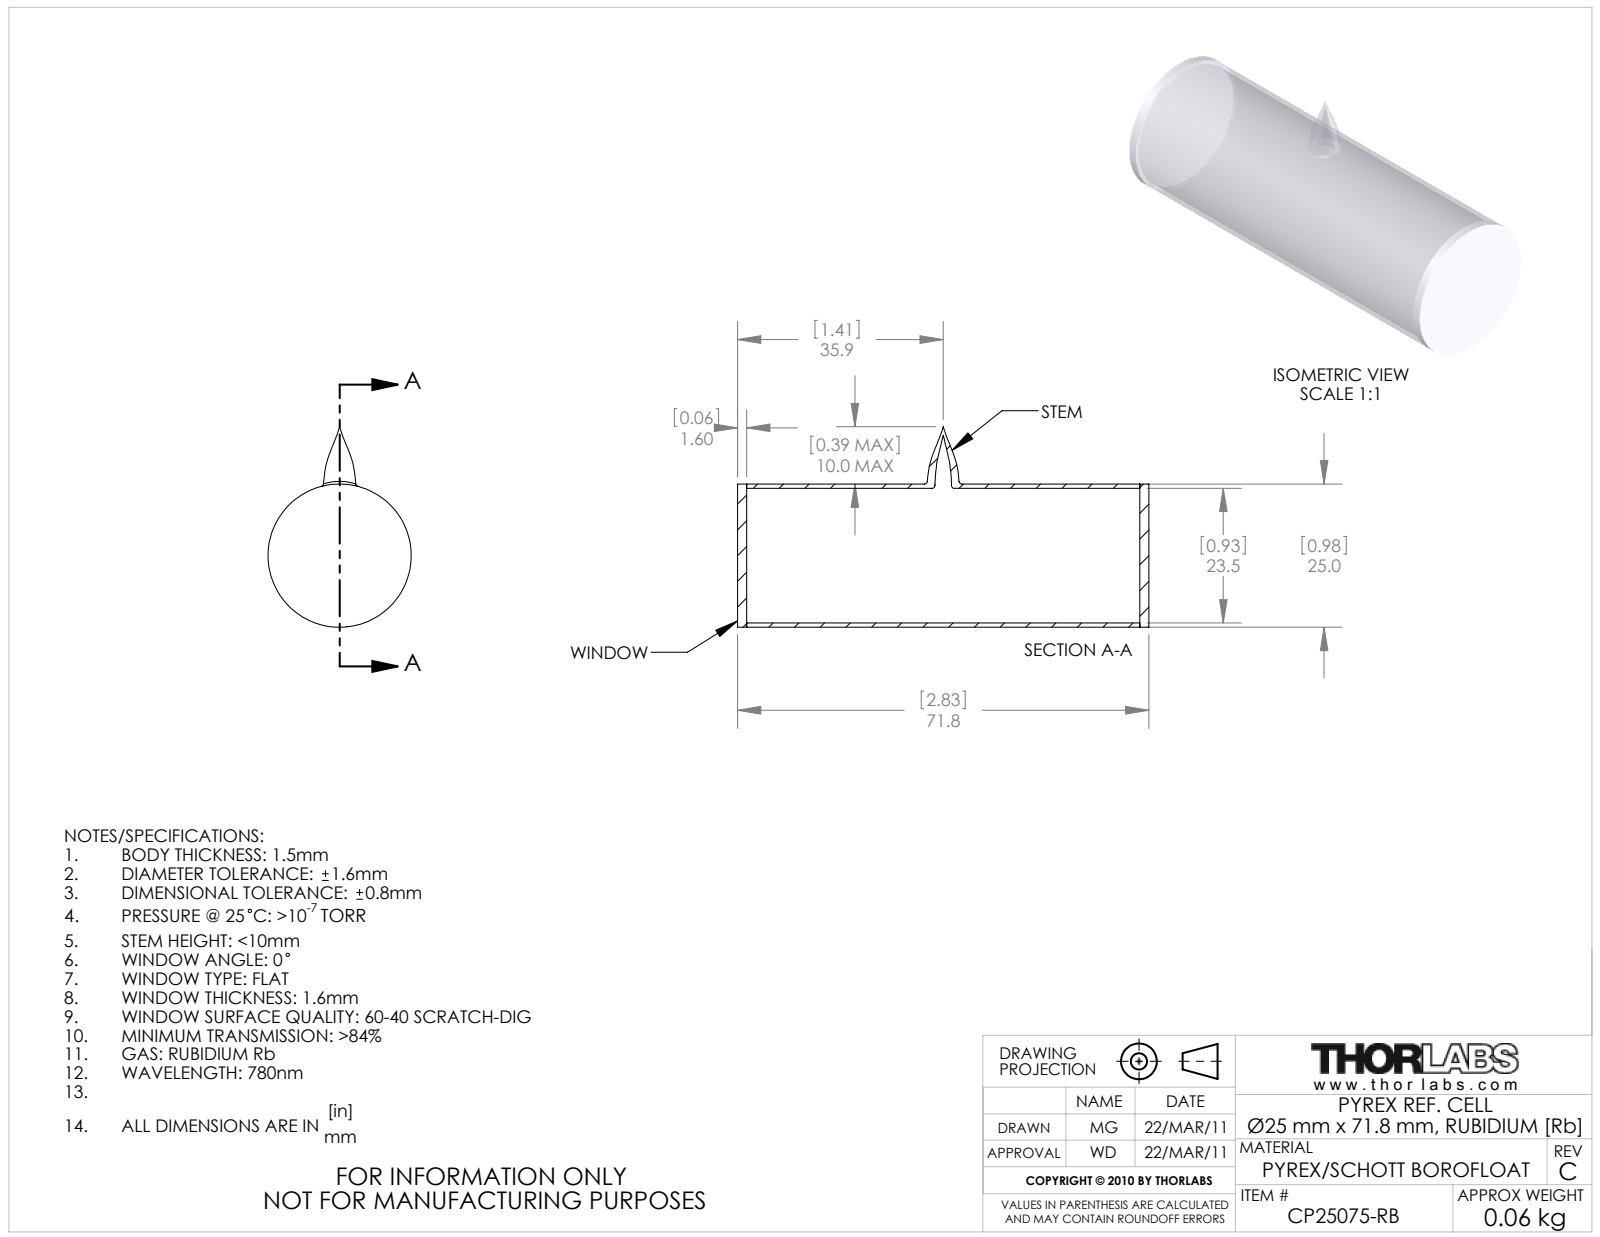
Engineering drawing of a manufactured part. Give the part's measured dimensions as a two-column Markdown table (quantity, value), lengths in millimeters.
| quantity | value |
| --- | --- |
| part name | 12093-E0W |
| STEP written by | SolidWorks 2009 (AUTOMOTIVE_DESIGN) |
| units | millimeters |
| bodies | 3 solids, 24 faces (6 planar, 10 cylindrical, 8 other) |
| overall size | 71.84 × 35 × 25 |
| volume | 5 577 mm³ |
| surface area | 12 920 mm² |
| round holes (diameter × count) | 2.91 × 1, 23.5 × 1 |
| round bosses / shafts (diameter × count) | 25 × 1 |
| main face-to-face distances | 1.6, 70.24, 68.64, 71.84 |
